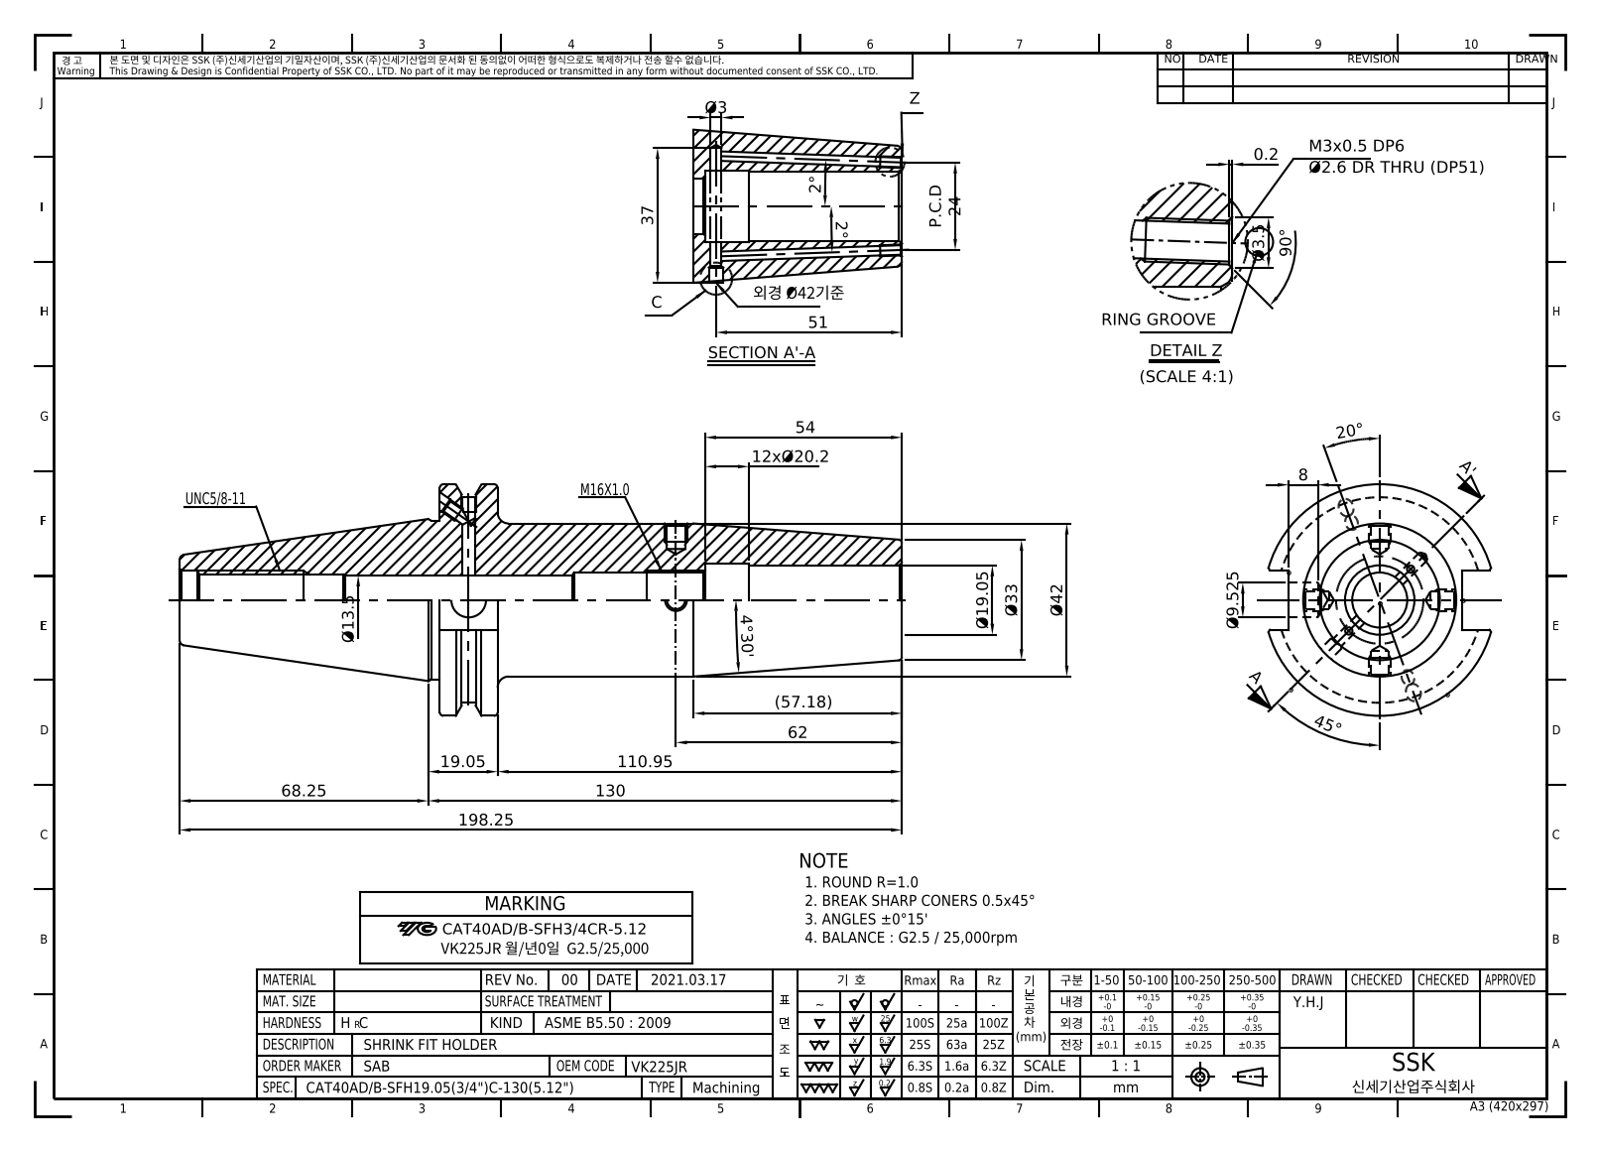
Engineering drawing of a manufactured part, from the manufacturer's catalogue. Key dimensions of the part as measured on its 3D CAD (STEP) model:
Part name (STEP PRODUCT): LO-CAT40ADB-SFH19.05CR-130
STEP written by: Autodesk Inventor 2022 (AUTOMOTIVE_DESIGN)
Units: millimetres
Bodies: 1 solid, 91 faces (37 planar, 31 cylindrical, 23 other)
Overall size (bounding box): 198.25 × 63.5 × 61.09
Volume: 213 579 mm³ · Surface area: 40 422 mm²
Round holes (diameter × count): ⌀3.24 ×4, ⌀2.46 ×2, ⌀4 ×2, ⌀4.2 ×2, ⌀9.53 ×1, ⌀13 ×1, ⌀13.39 ×1, ⌀14.92 ×1, ⌀16.3 ×1, ⌀19.05 ×1, ⌀20.2 ×1
Round bosses / shafts (diameter × count): ⌀63.5 ×1, ⌀43.6 ×1, ⌀42 ×1
Partial cylindrical surfaces — rounded edges, fillets, slot ends (radius × count): R28.15 ×1
Main face-to-face distances: 15.88, 126.83, 110.95, 47.6, 16.38, 71.42, 87.3, 198.25, 144.25, 72.83
